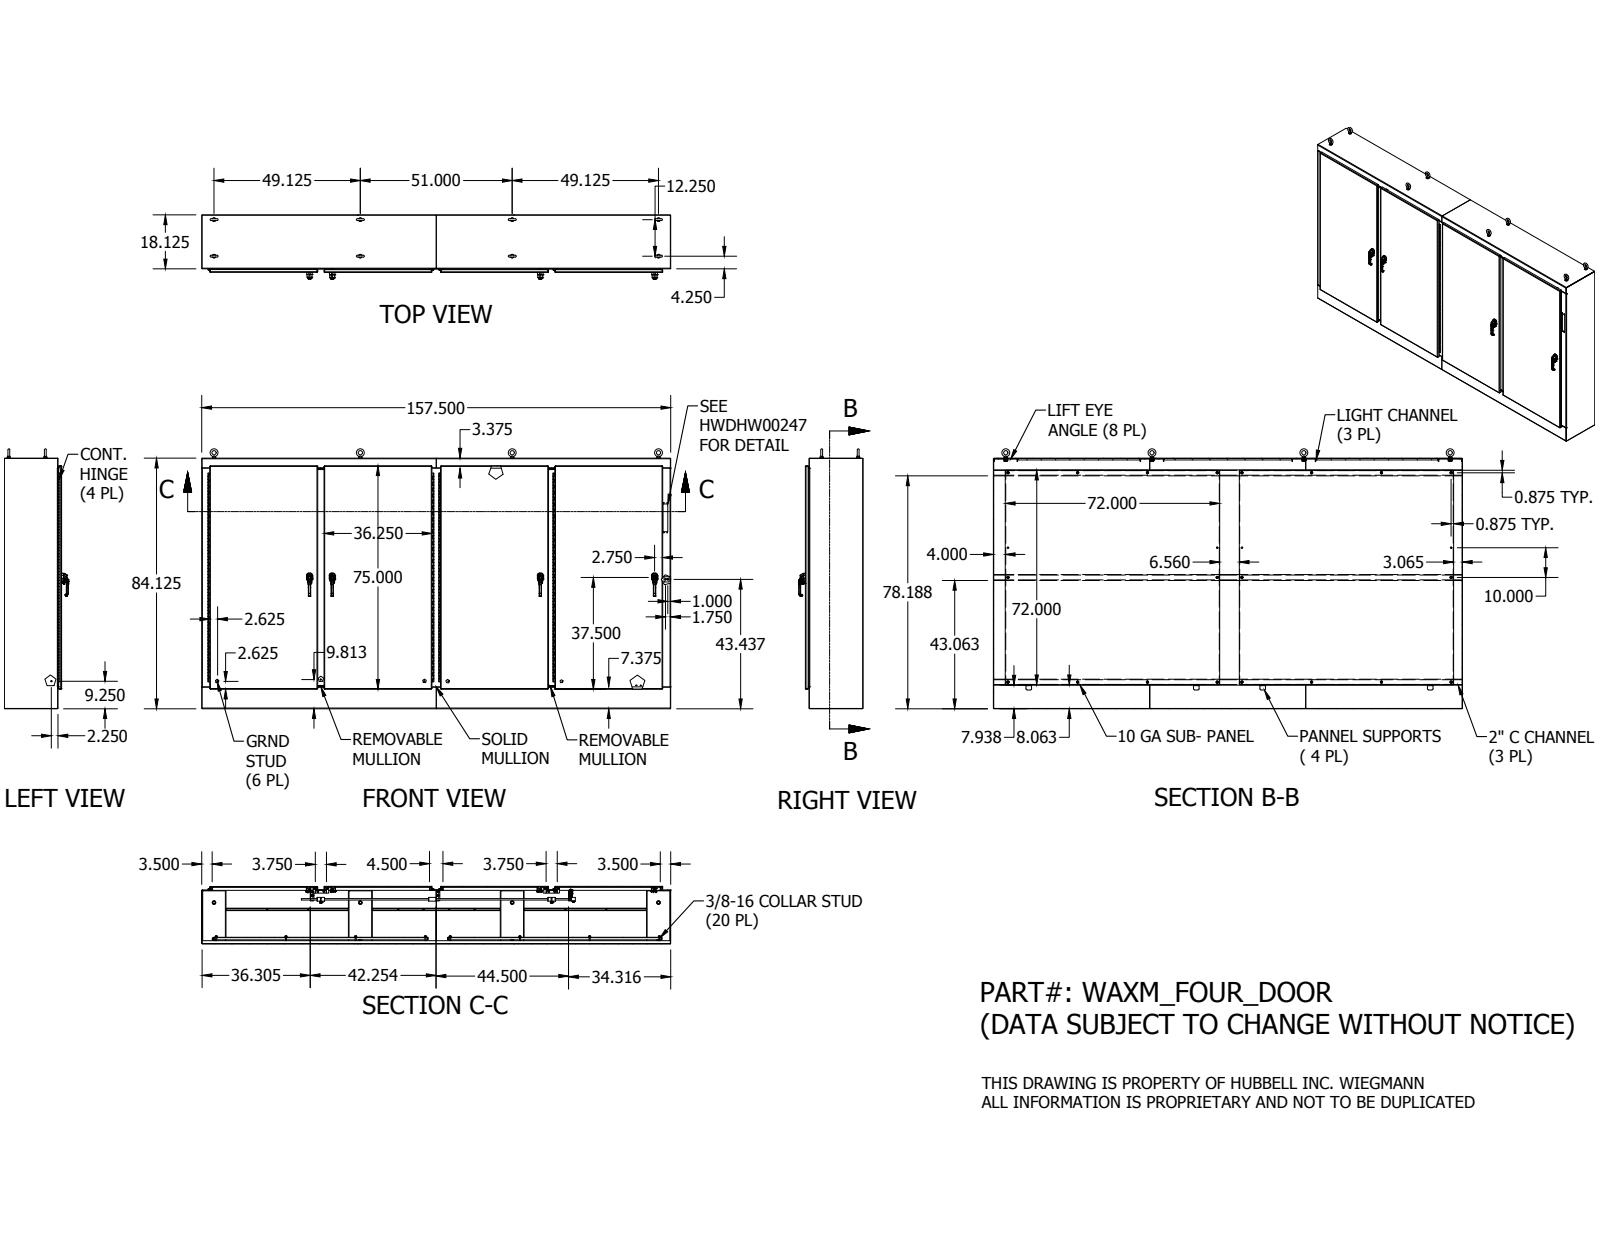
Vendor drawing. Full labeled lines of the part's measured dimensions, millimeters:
Part name (STEP PRODUCT): WAXMU_FOUR_DOOR_LARGE_BACK; WAXMU_FOUR_DOOR_SMALL_BACK; HFW1404-WAM4EWU; 3889 (+8 more)
STEP written by: Autodesk Inventor 2014 (AUTOMOTIVE_DESIGN)
Units: millimetres
Bodies: 467 solids, 18032 faces (8300 planar, 5816 cylindrical, 3916 other)
Overall size (bounding box): 4000.5 × 2216.09 × 548.73
Volume: 111 100 000 mm³ · Surface area: 69 820 000 mm²
Round holes (diameter × count): ⌀6.35 ×34, ⌀9.52 ×34, ⌀7.02 ×24, ⌀14.29 ×24, ⌀7.8 ×20, ⌀4.83 ×16, ⌀5.08 ×16, ⌀7.33 ×16, ⌀8.51 ×16, ⌀9.65 ×16, ⌀7.94 ×14, ⌀7.14 ×13
Round bosses / shafts (diameter × count): ⌀8.38 ×40, ⌀6.35 ×37, ⌀15.88 ×27, ⌀9.52 ×25, ⌀8.56 ×23, ⌀12.7 ×17, ⌀7.11 ×16, ⌀14.29 ×15
Partial cylindrical surfaces — rounded edges, fillets, slot ends (radius × count): R0.5 ×700, R0.3 ×417, R0.51 ×384, R0.47 ×86, R1.27 ×70, R1.59 ×56, R2 ×55, R1.5 ×45
Main face-to-face distances: 3.18, 3.17, 434.46, 1.59, 50.8, 57.15, 53.98, 53.97, 488.43, 485.26
Hole centre spacings: 1784.35, 1.6, 1880.87, 2.53, 1995.42, 594.78, 1247.77, 1285.98
